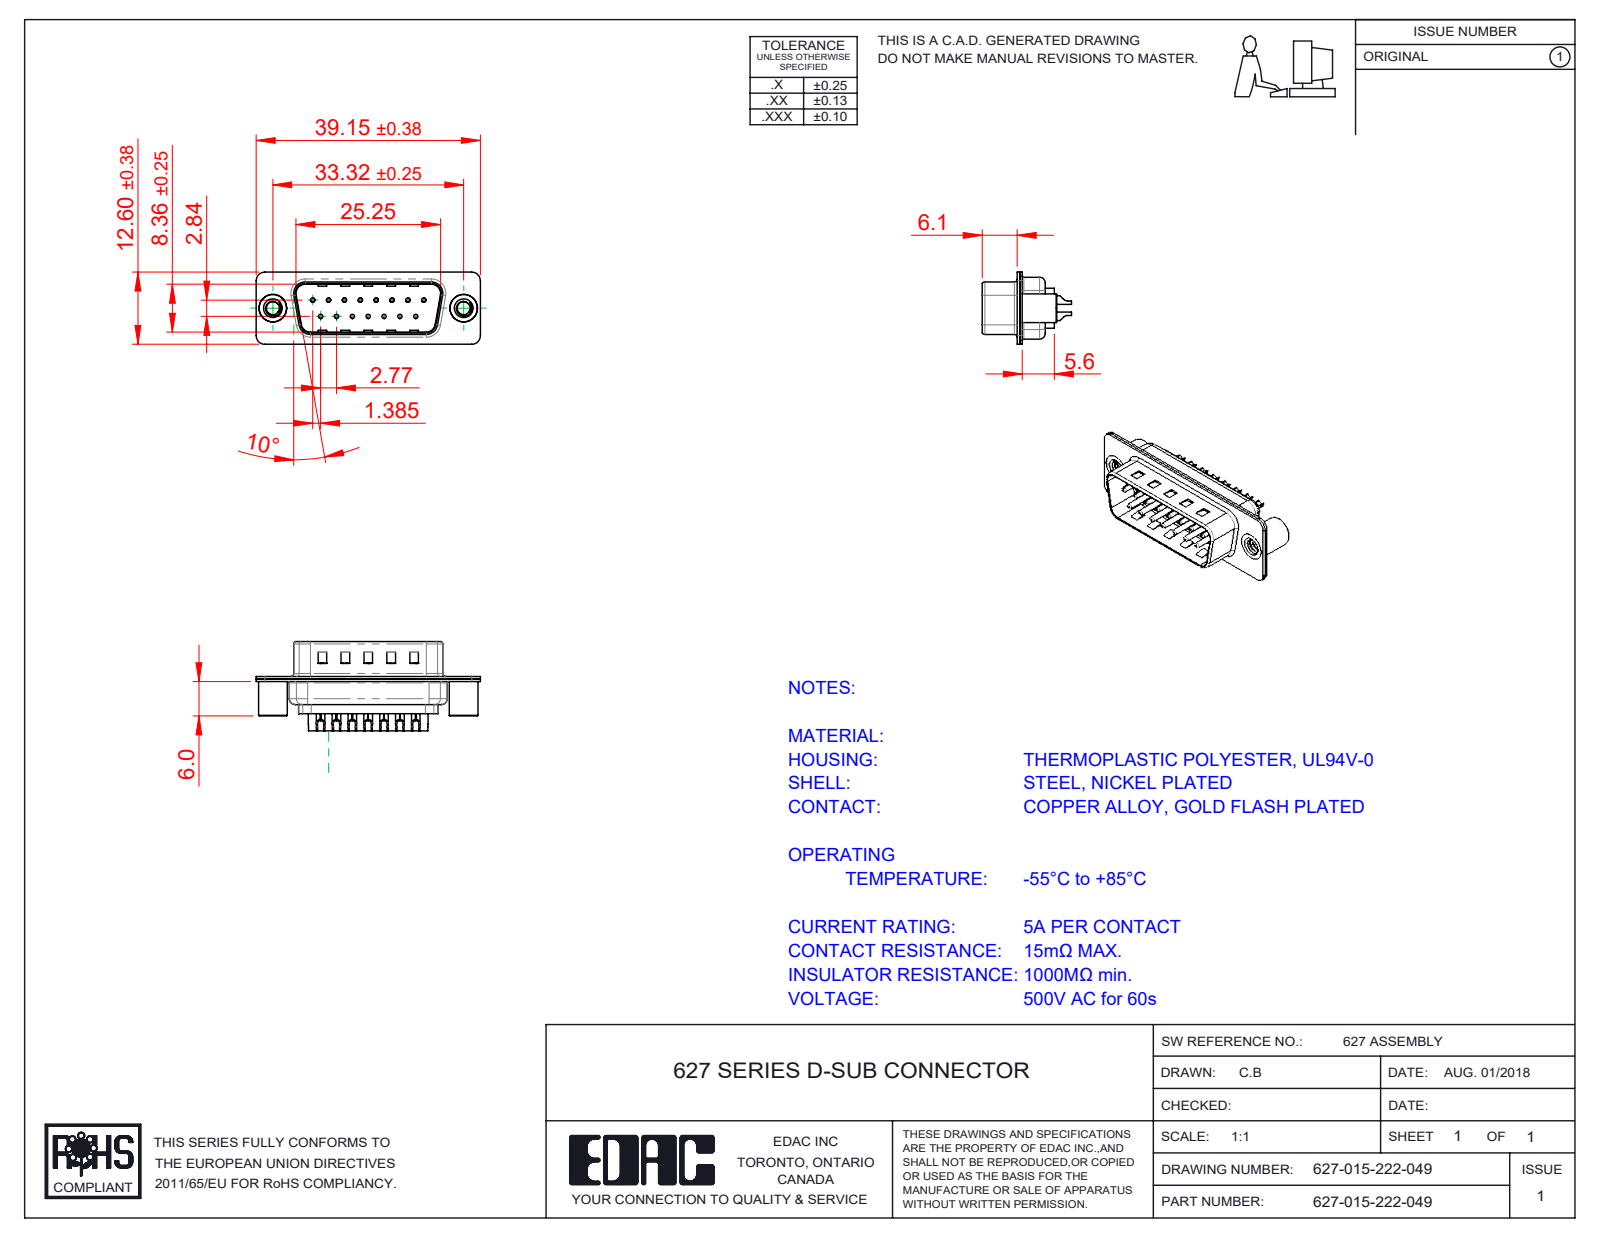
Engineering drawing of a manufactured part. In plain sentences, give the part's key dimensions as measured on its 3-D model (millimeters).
The part is named "627 Contact Row 1_22L; 627 Housing_15 LP; 627 Shell Rear_15 Contacts; 627 4-40 Threaded Standoff BS (+3 more)". Its 3-D file was written by "SolidWorks 2020 (CONFIG_CONTROL_DESIGN)". It is 20 solids with 1322 faces: 349 planar, 588 cylindrical and 385 other. Overall it measures 39.15 by 15.35 by 12.6 millimeters. Its volume is 1 932 cubic millimeters and its surface area 5 614 square millimeters. Round holes: 15 of diameter 0.35, 15 of diameter 1.1, 15 of diameter 1.6, 2 of diameter 2.26, 2 of diameter 4, 2 of diameter 4.8. Round bosses or shafts: 15 of diameter 2, 15 of diameter 1.5, 15 of diameter 0.75, 2 of diameter 5, 2 of diameter 4.9. Partial cylindrical surfaces (rounded edges, fillets, slot ends): 16 of radius 1.5, 12 of radius 2, 8 of radius 0.5, 8 of radius 1.6, 6 of radius 1, 4 of radius 0.25, 4 of radius 0.6, 4 of radius 0.65. The main face-to-face distances are 0.4, 0.45, 0.9, 0.82, 9.58, 8.76, 1.5, 1.4, 6.5, 5.6. The hole center spacings are 3.16, 2.77, 5.54, 8.31, 11.08, 5.03, 5.04, 7.48.
